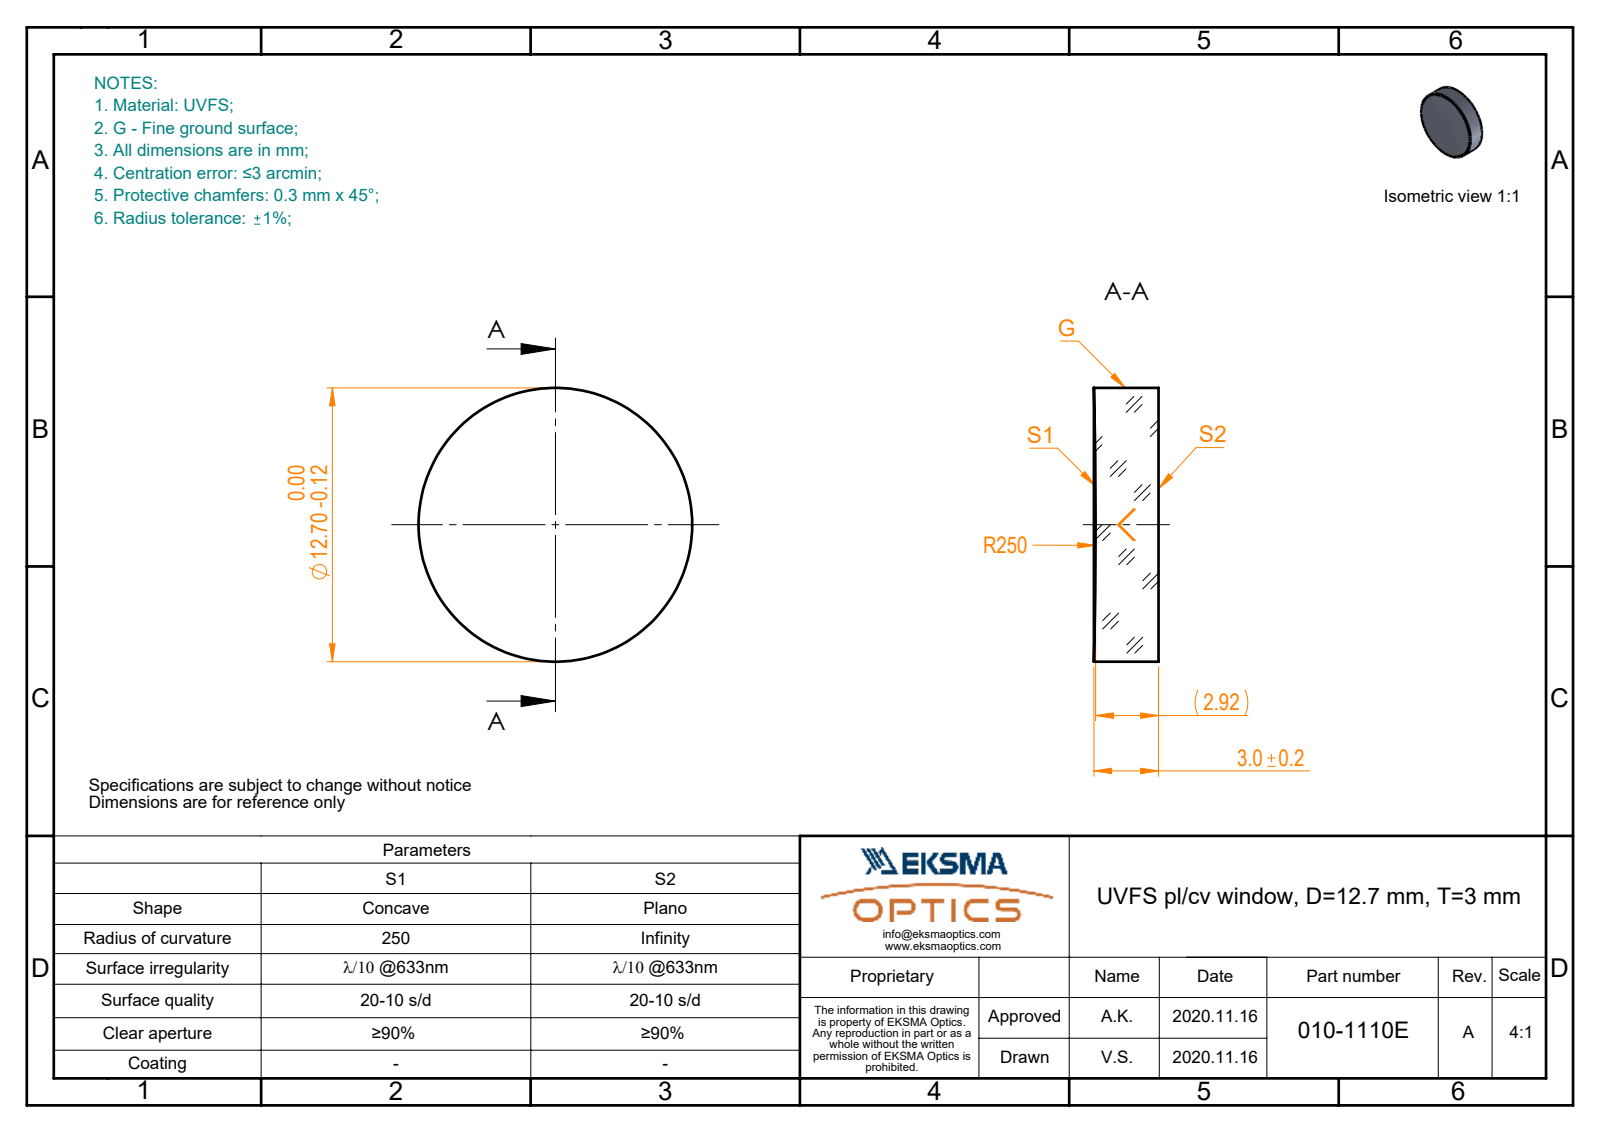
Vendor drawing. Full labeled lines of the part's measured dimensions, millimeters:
Part name (STEP PRODUCT): 010-1110E_UVFS_PCV_window
STEP written by: SolidWorks 2019 (CONFIG_CONTROL_DESIGN)
Units: millimetres
Bodies: 1 solid, 5 faces (1 planar, 2 cylindrical, 2 other)
Overall size (bounding box): 12.7 × 12.7 × 3
Volume: 375 mm³ · Surface area: 373 mm²
Round bosses / shafts (diameter × count): ⌀12.7 ×1
